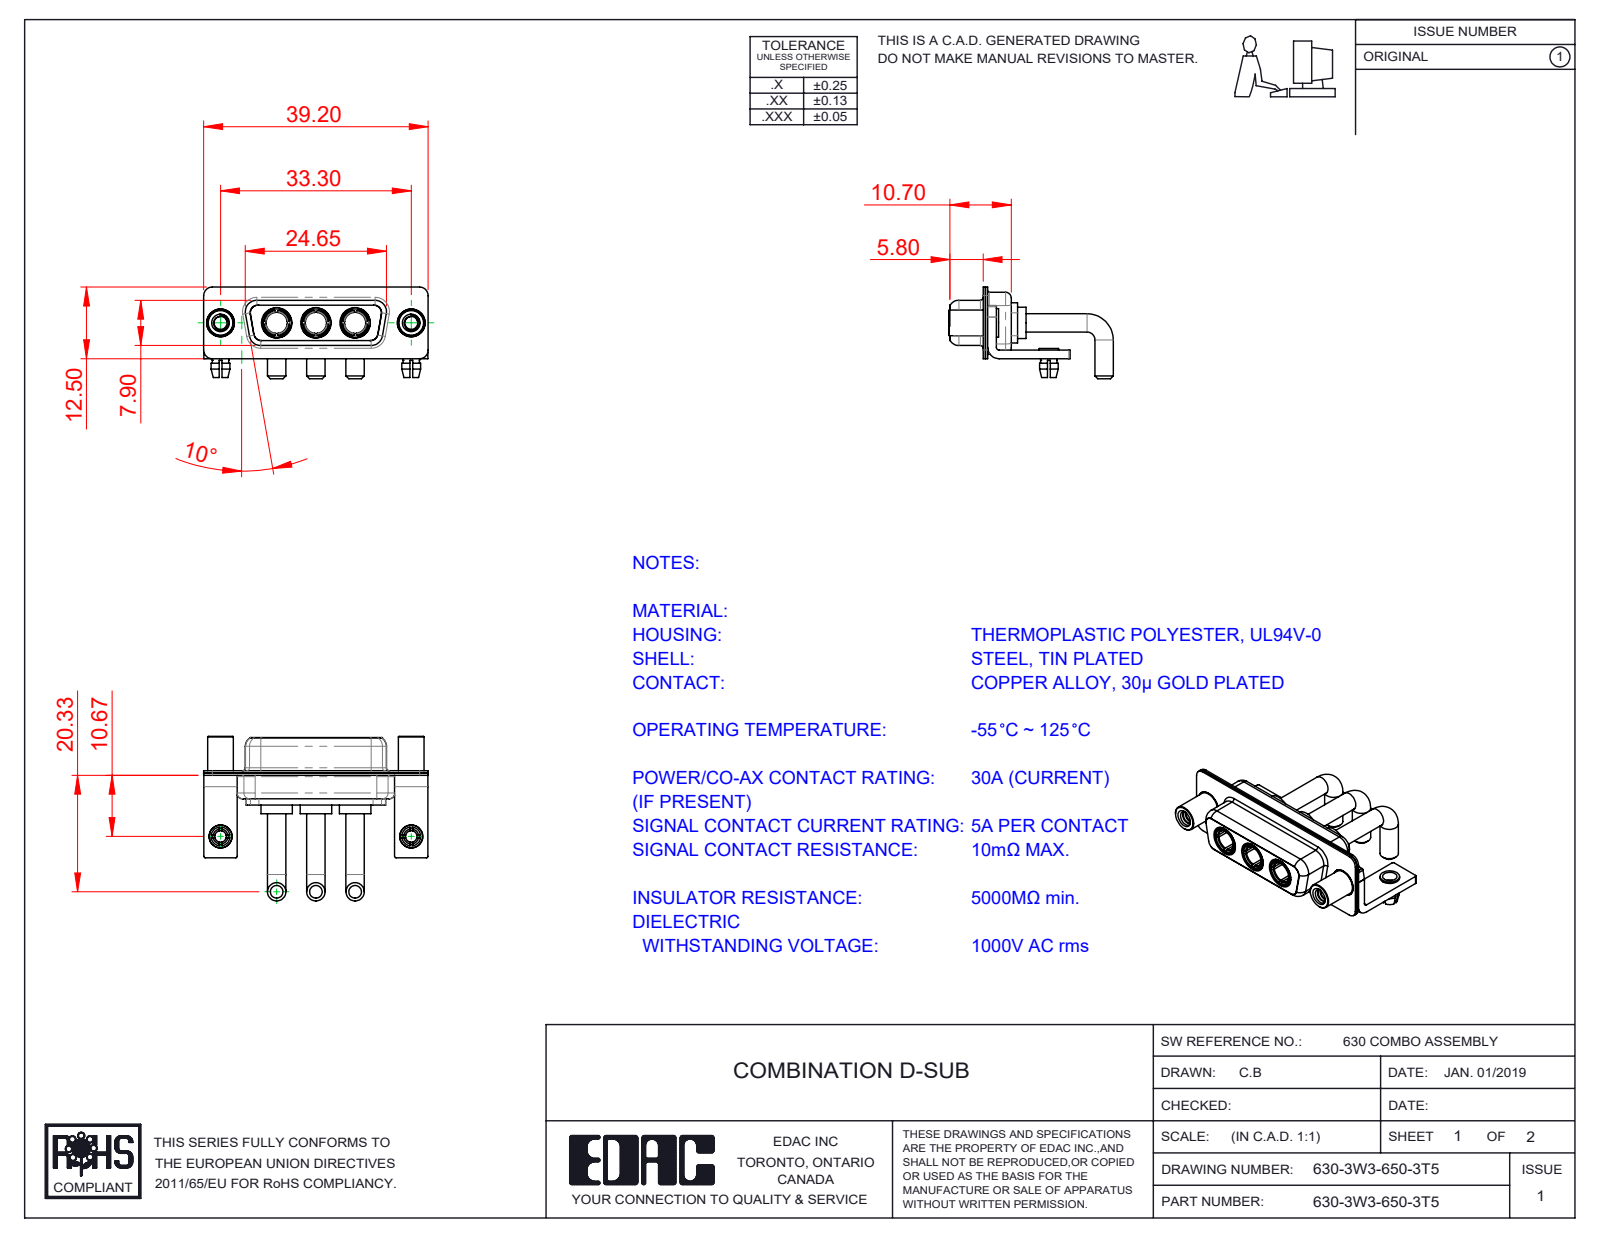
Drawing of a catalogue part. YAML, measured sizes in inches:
part_name: "630Combo Shell Front_15 Contacts; 630-3W3-650-3T5; 630Combo Threaded Standoff_5; Power Socket_Ext 30A RA (+4 more)"
step_written_by: "SolidWorks 2020 (CONFIG_CONTROL_DESIGN)"
units: inches
bodies: {solids: 15, faces: 693, planar: 224, cylindrical: 304, other: 165}
overall_size: [1.543, 1.131, 0.63]
volume: 0.203
surface_area: 11.35
round_holes:
  - {diameter: 0.191, count: 5}
  - {diameter: 0.146, count: 3}
  - {diameter: 0.209, count: 3}
  - {diameter: 0.079, count: 2}
  - {diameter: 0.089, count: 2}
  - {diameter: 0.098, count: 2}
  - {diameter: 0.126, count: 2}
  - {diameter: 0.157, count: 2}
  - {diameter: 0.159, count: 2}
round_bosses_or_shafts:
  - {diameter: 0.126, count: 6}
  - {diameter: 0.217, count: 3}
  - {diameter: 0.205, count: 3}
  - {diameter: 0.195, count: 3}
  - {diameter: 0.187, count: 3}
  - {diameter: 0.148, count: 3}
  - {diameter: 0.197, count: 2}
  - {diameter: 0.195, count: 2}
partial_cylinders:
  - {radius: 0.01, count: 16}
  - {radius: 0.059, count: 16}
  - {radius: 0.079, count: 13}
  - {radius: 0.053, count: 12}
  - {radius: 0.063, count: 8}
  - {radius: 0.02, count: 5}
  - {radius: 0.024, count: 4}
  - {radius: 0.026, count: 4}
face_to_face_distances: [0.016, 0.031, 0.055, 0.018, 0.059, 0.333, 0.071, 0.35, 0.278, 0.205]
hole_center_spacings: [0.27, 0.386, 0.656, 0.925, 1.311, 0.539]
